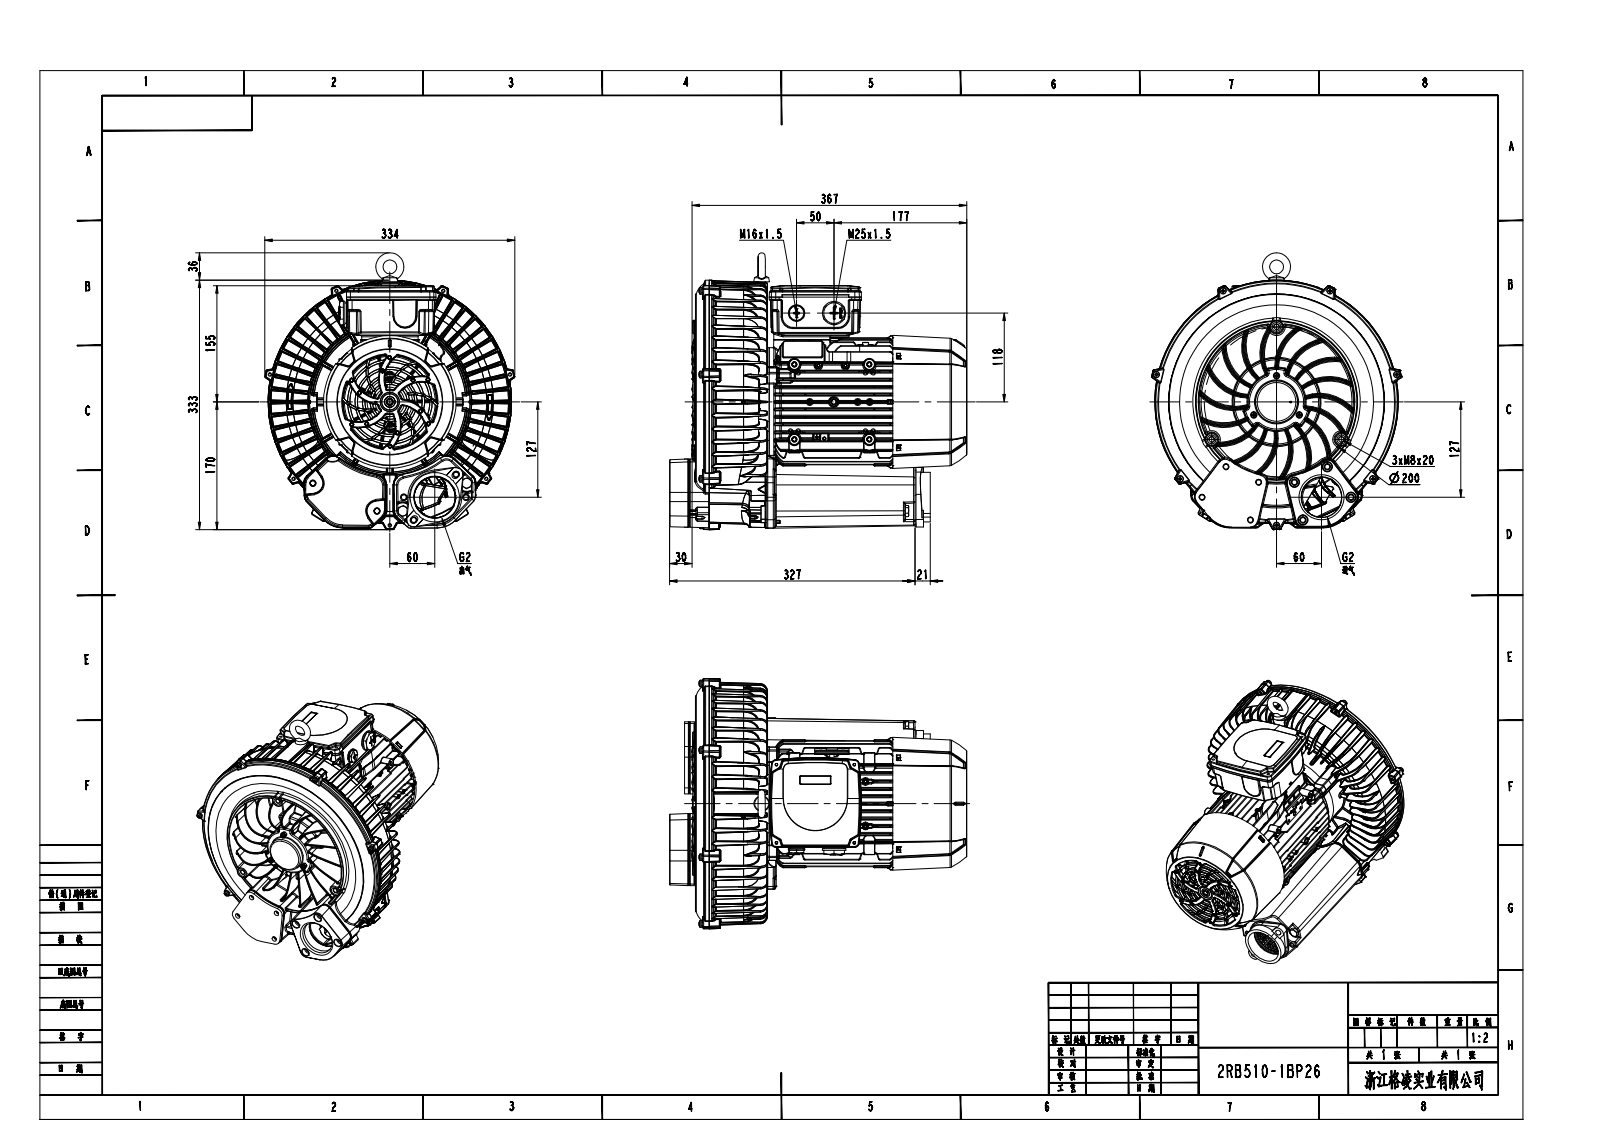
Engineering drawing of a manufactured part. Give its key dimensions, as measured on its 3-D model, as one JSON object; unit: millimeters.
{"part_name": "2RB510-1BP26", "step_written_by": "PRO/ENGINEER BY PARAMETRIC TECHNOLOGY CORPORATION, 2007090 (AUTOMOTIVE_DESIGN_CC2)", "units": "millimeters", "bodies": {"solids": 1, "faces": 123, "planar": 58, "cylindrical": 57, "other": 8}, "overall_size": [396.7, 368.92, 340], "volume_mm3": 18480000, "surface_area_mm2": 569064, "round_holes": [[6.8, 3], [54.11, 1], [56.5, 1]], "round_bosses_or_shafts": [[340, 1], [177, 1], [66.3, 1]], "partial_cylinders_radius": [[4.25, 4], [7, 4], [10, 4], [11, 4], [14, 4], [499.89, 3], [7.5, 2], [9, 2]], "face_to_face_distances": [100, 266.2, 366.2, 11.6, 254.6, 111.6, 376.7, 122.1, 110.5, 10.5], "hole_center_spacings": [173.2, 81.47, 165.59, 234.8, 120]}
